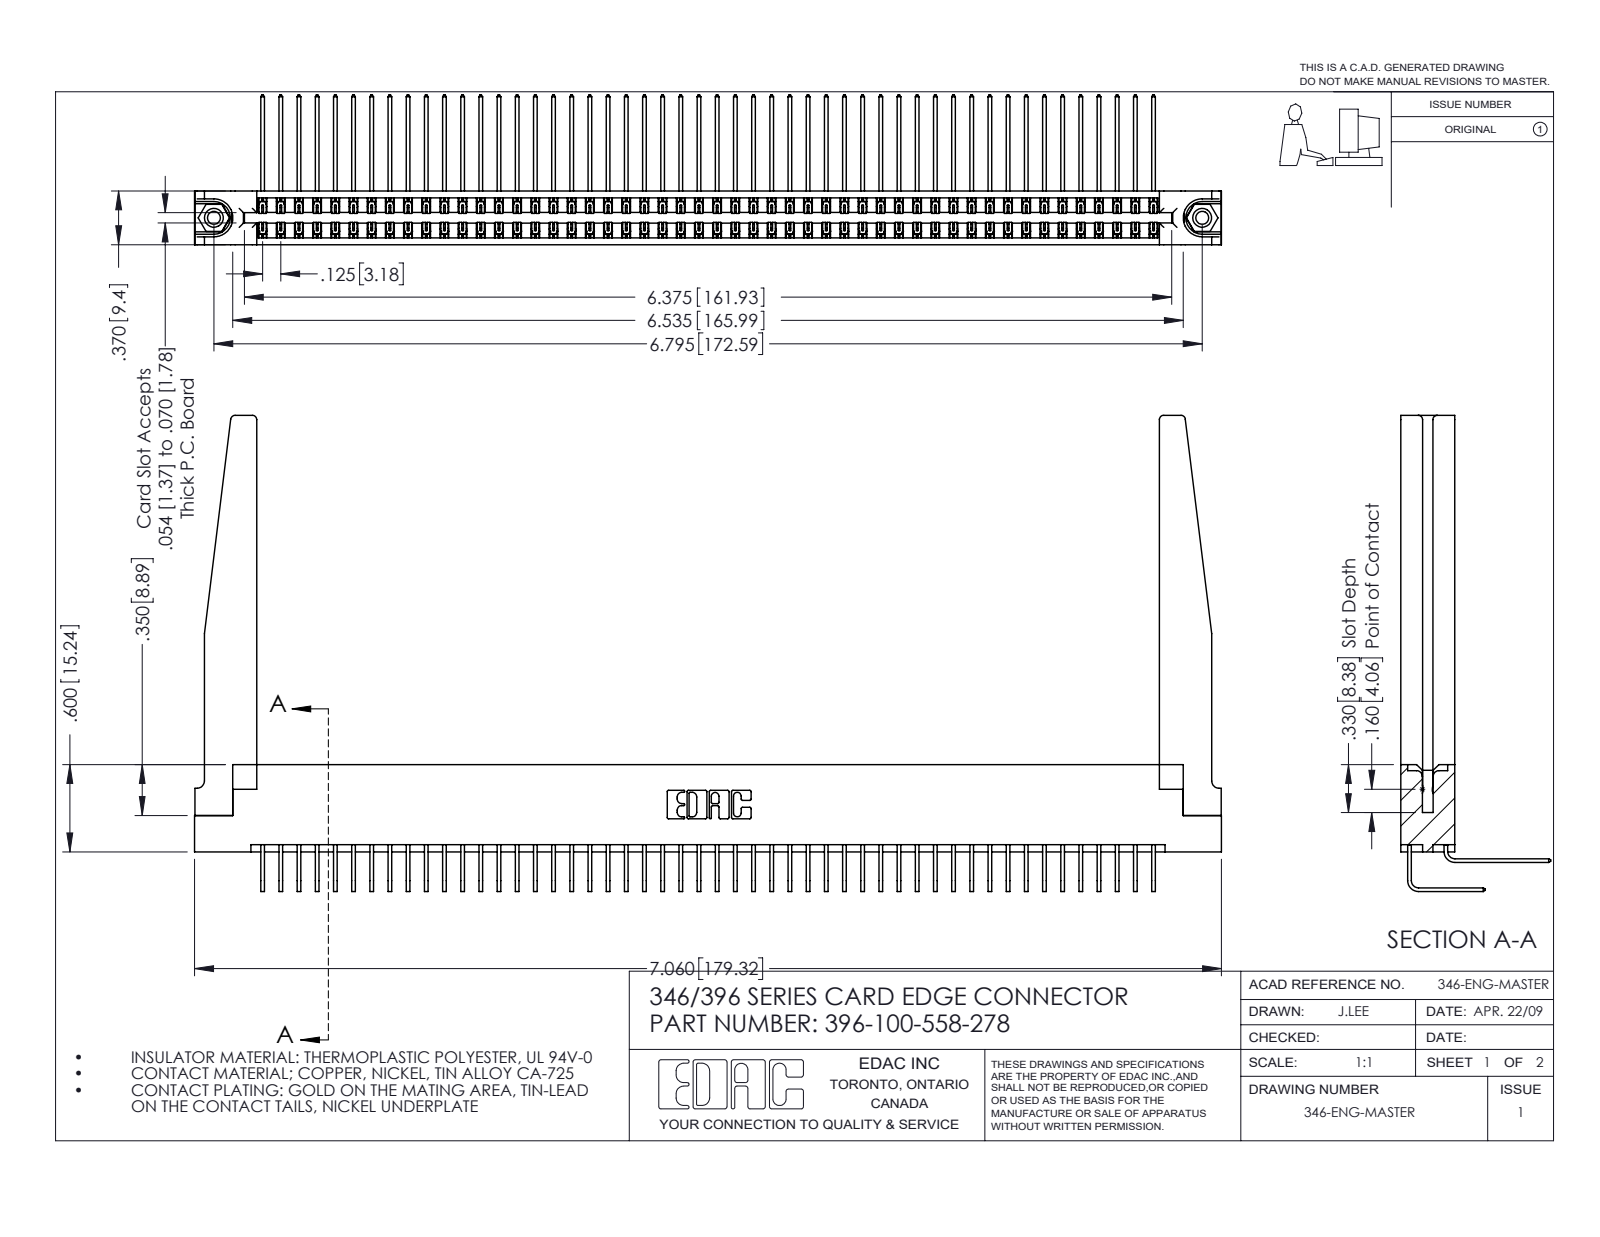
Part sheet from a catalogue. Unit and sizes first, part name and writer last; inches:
Units: inches
Overall size (bounding box): 7.06 × 3.273 × 1.03
Round holes (diameter × count): ⌀0.089 ×2, ⌀0.125 ×2, ⌀0.156 ×2, ⌀0.064 ×1
Round bosses / shafts (diameter × count): ⌀0.155 ×2
Partial cylindrical surfaces — rounded edges, fillets, slot ends (radius × count): R0.006 ×150, R0.01 ×22, R0.03 ×8, R0.007 ×6, R0.031 ×6, R0.05 ×4, R0.026 ×3, R0.014 ×2
Main face-to-face distances: 0.322, 0.048, 0.37, 0.072, 0.025, 0.298, 0.25, 0.148, 0.15, 0.275
Hole centre spacings: 0.246, 6.586, 6.795
Volume: 1.528 in³ · Surface area: 53.24 in²
Bodies: 105 solids, 5756 faces (3918 planar, 1786 cylindrical, 52 other)
Part name (STEP PRODUCT): 346 Part_Flush Mounting Lugs - 0.156 Dia-TH; 345-250-001_345-250-001-102; 346-220-078_345-220-078; 396-100-558-278 (+2 more)
STEP written by: SolidWorks 2016 (CONFIG_CONTROL_DESIGN)
